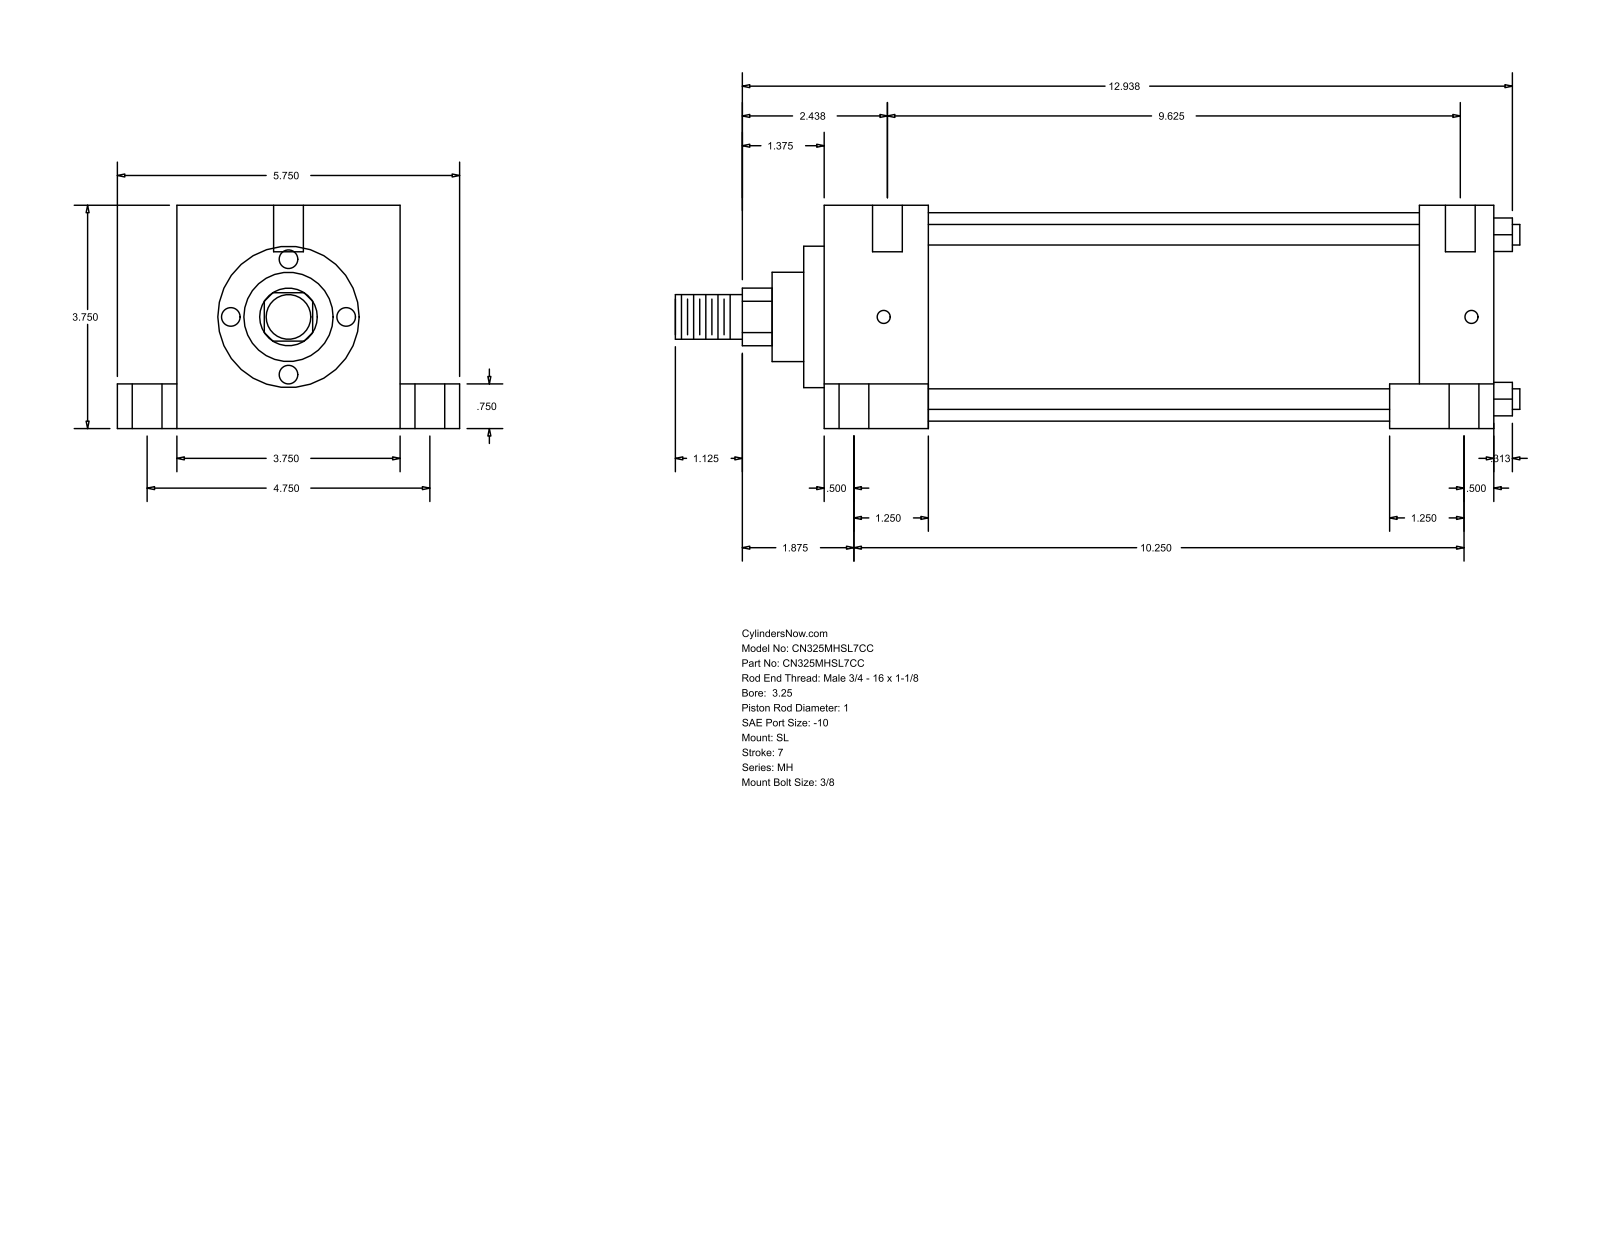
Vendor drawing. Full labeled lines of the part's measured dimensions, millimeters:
Part name (STEP PRODUCT): MH_SL__0325_1
STEP written by: GSSL Pune (CONFIG_CONTROL_DESIGN)
Units: millimetres
Bodies: 0 solids, 110 faces (77 planar, 33 cylindrical, 0 other)
Overall size (bounding box): 360.36 × 146.05 × 95.25
Round holes (diameter × count): ⌀12.7 ×6, ⌀5.56 ×4, ⌀19.05 ×4
Round bosses / shafts (diameter × count): ⌀8.76 ×4, ⌀88.9 ×1, ⌀60.33 ×1, ⌀38.1 ×1, ⌀25.4 ×1, ⌀19.05 ×1
Partial cylindrical surfaces — rounded edges, fillets, slot ends (radius × count): R12.29 ×1
Main face-to-face distances: 95.24, 285.76, 44.46, 241.3, 25.41, 120.65, 19.05, 76.19, 254.01, 209.55
Hole centre spacings: 60.35, 60.41, 61.65, 62, 120.66, 250.82, 253.36, 254.89
